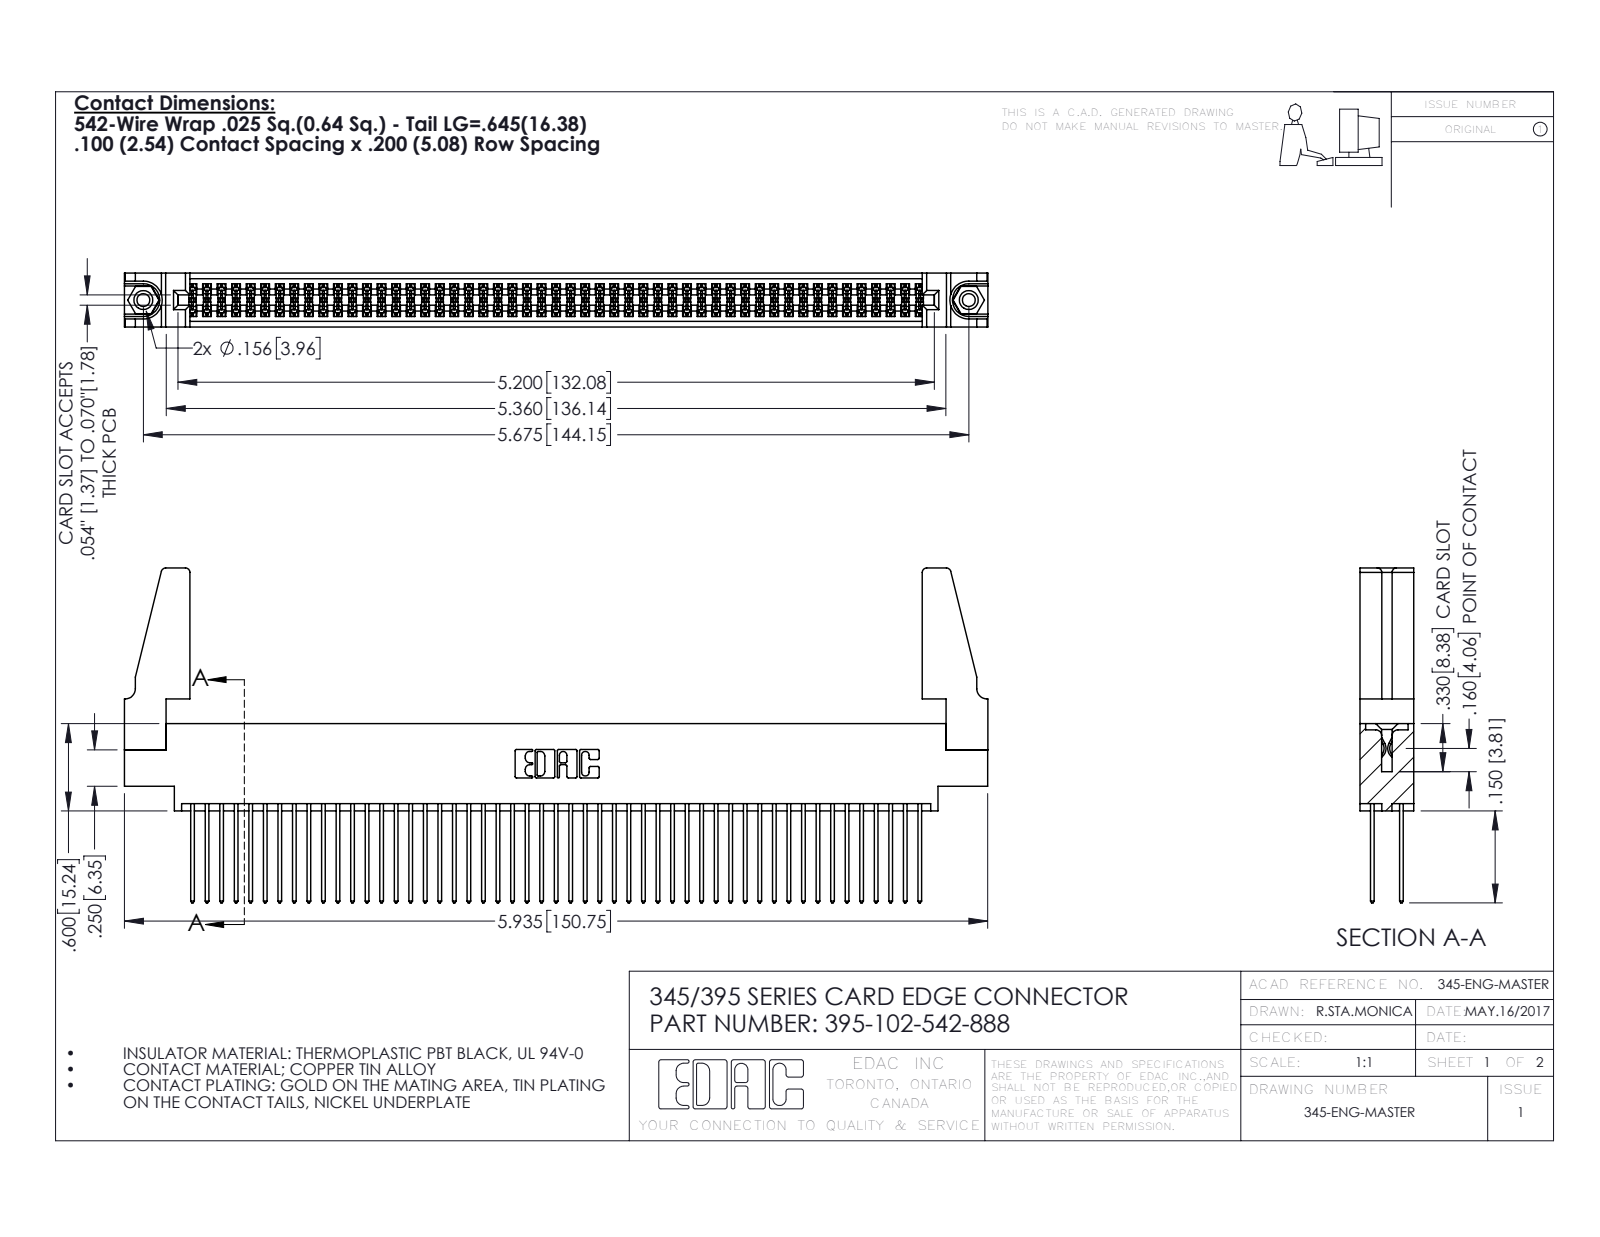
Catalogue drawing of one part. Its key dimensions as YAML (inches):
part_name: "345 Part_0.170 Offset - 0.156 Dia-TH; 345-292-001_345-293-142; 395-102-542-888; 345-250-001_345-250-001-102 (+1 more)"
step_written_by: "SolidWorks 2016 (CONFIG_CONTROL_DESIGN)"
units: inches
bodies: {solids: 107, faces: 5354, planar: 3522, cylindrical: 1816, other: 16}
overall_size: [5.936, 2.302, 0.37]
volume: 1.119
surface_area: 43.35
round_holes:
  - {diameter: 0.089, count: 2}
  - {diameter: 0.125, count: 2}
  - {diameter: 0.156, count: 2}
  - {diameter: 0.064, count: 1}
round_bosses_or_shafts:
  - {diameter: 0.155, count: 2}
partial_cylinders:
  - {radius: 0.006, count: 153}
  - {radius: 0.01, count: 102}
  - {radius: 0.01, count: 22}
  - {radius: 0.03, count: 8}
  - {radius: 0.007, count: 6}
  - {radius: 0.031, count: 6}
  - {radius: 0.026, count: 3}
  - {radius: 0.014, count: 2}
face_to_face_distances: [0.072, 0.298, 0.2, 0.098, 0.272, 0.025, 0.37, 0.225, 0.175, 0.149]
hole_center_spacings: [0.27, 5.439, 5.675]
